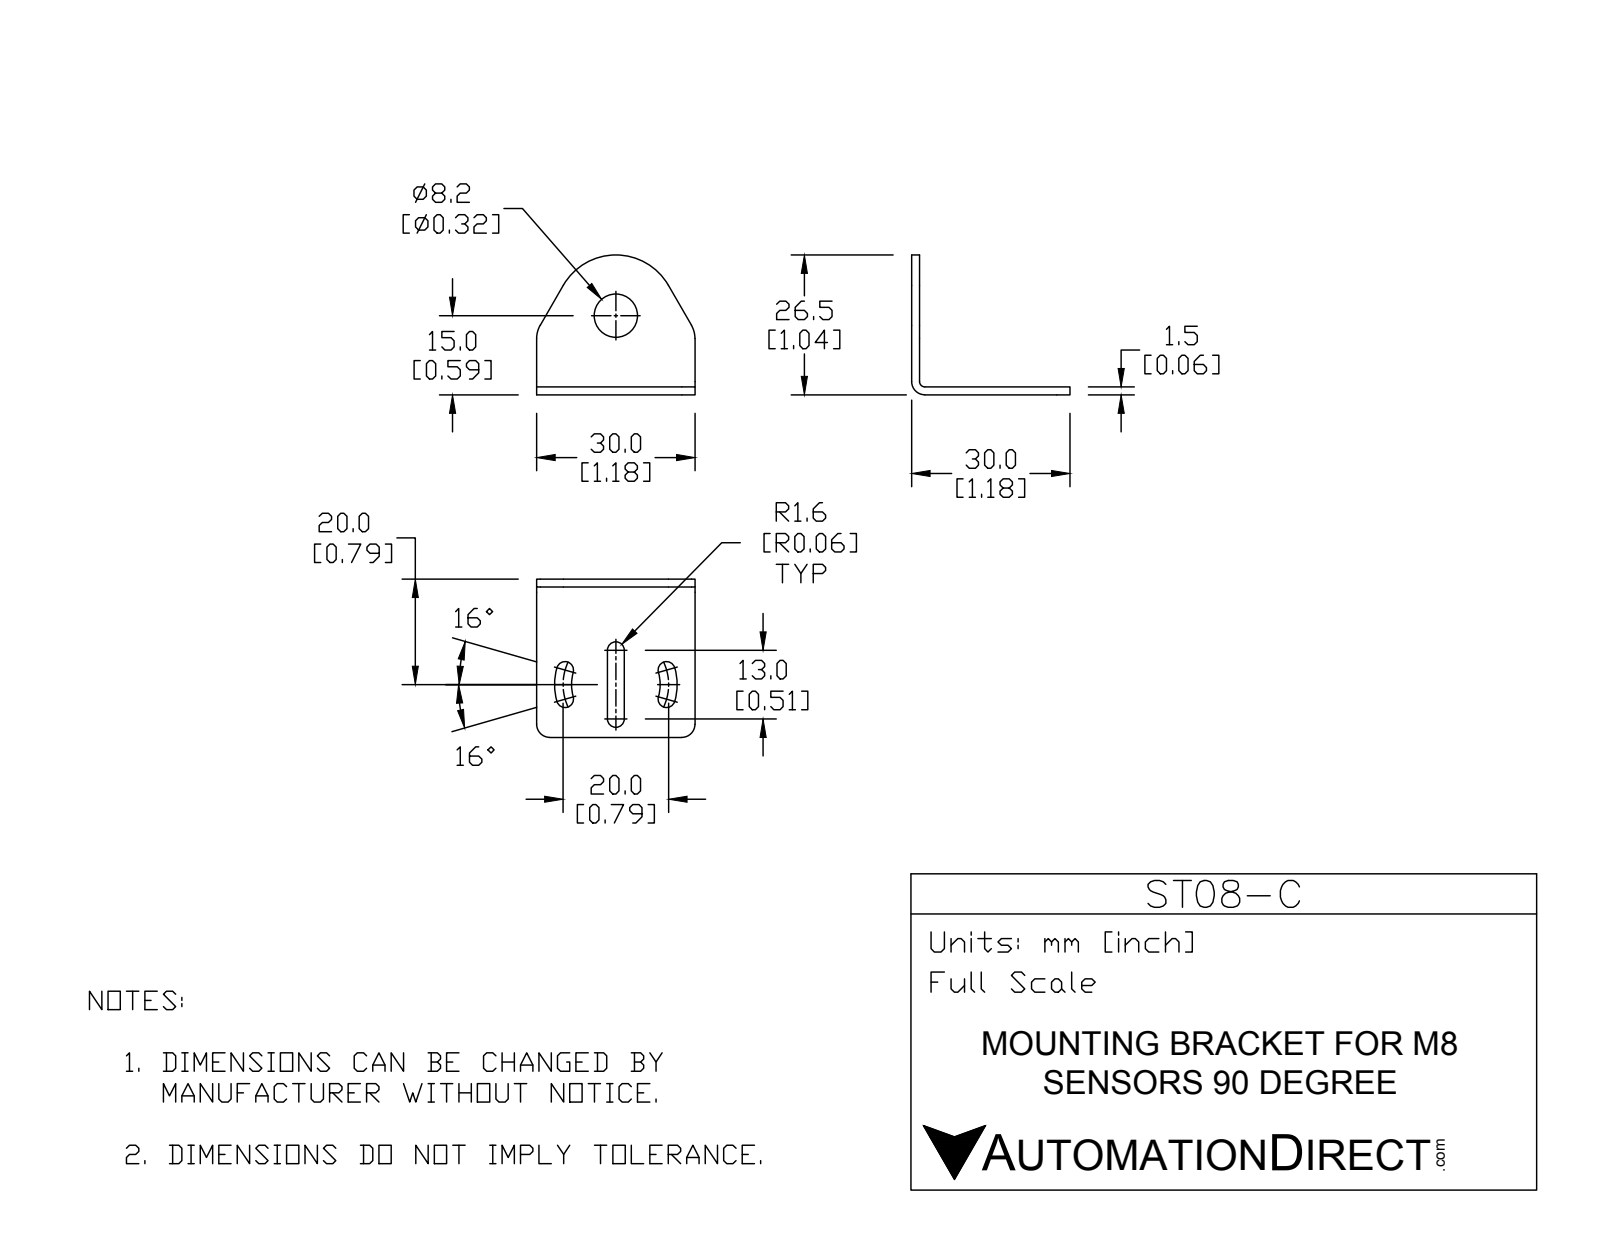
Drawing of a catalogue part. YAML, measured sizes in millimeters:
part_name: "ST08-C"
step_written_by: "SolidWorks 2015 (CONFIG_CONTROL_DESIGN)"
units: millimeters
bodies: {solids: 1, faces: 38, planar: 15, cylindrical: 23, other: 0}
overall_size: [30, 30, 26.5]
volume: 1994
surface_area: 3042
round_holes:
  - {diameter: 8.2, count: 1}
partial_cylinders:
  - {radius: 1.6, count: 6}
  - {radius: 2, count: 2}
  - {radius: 5, count: 2}
  - {radius: 1.5, count: 1}
  - {radius: 3, count: 1}
  - {radius: 8.4, count: 1}
  - {radius: 11.48, count: 1}
  - {radius: 11.6, count: 1}
face_to_face_distances: [1.5, 30, 28.5, 13.4, 16.6, 3.2]
